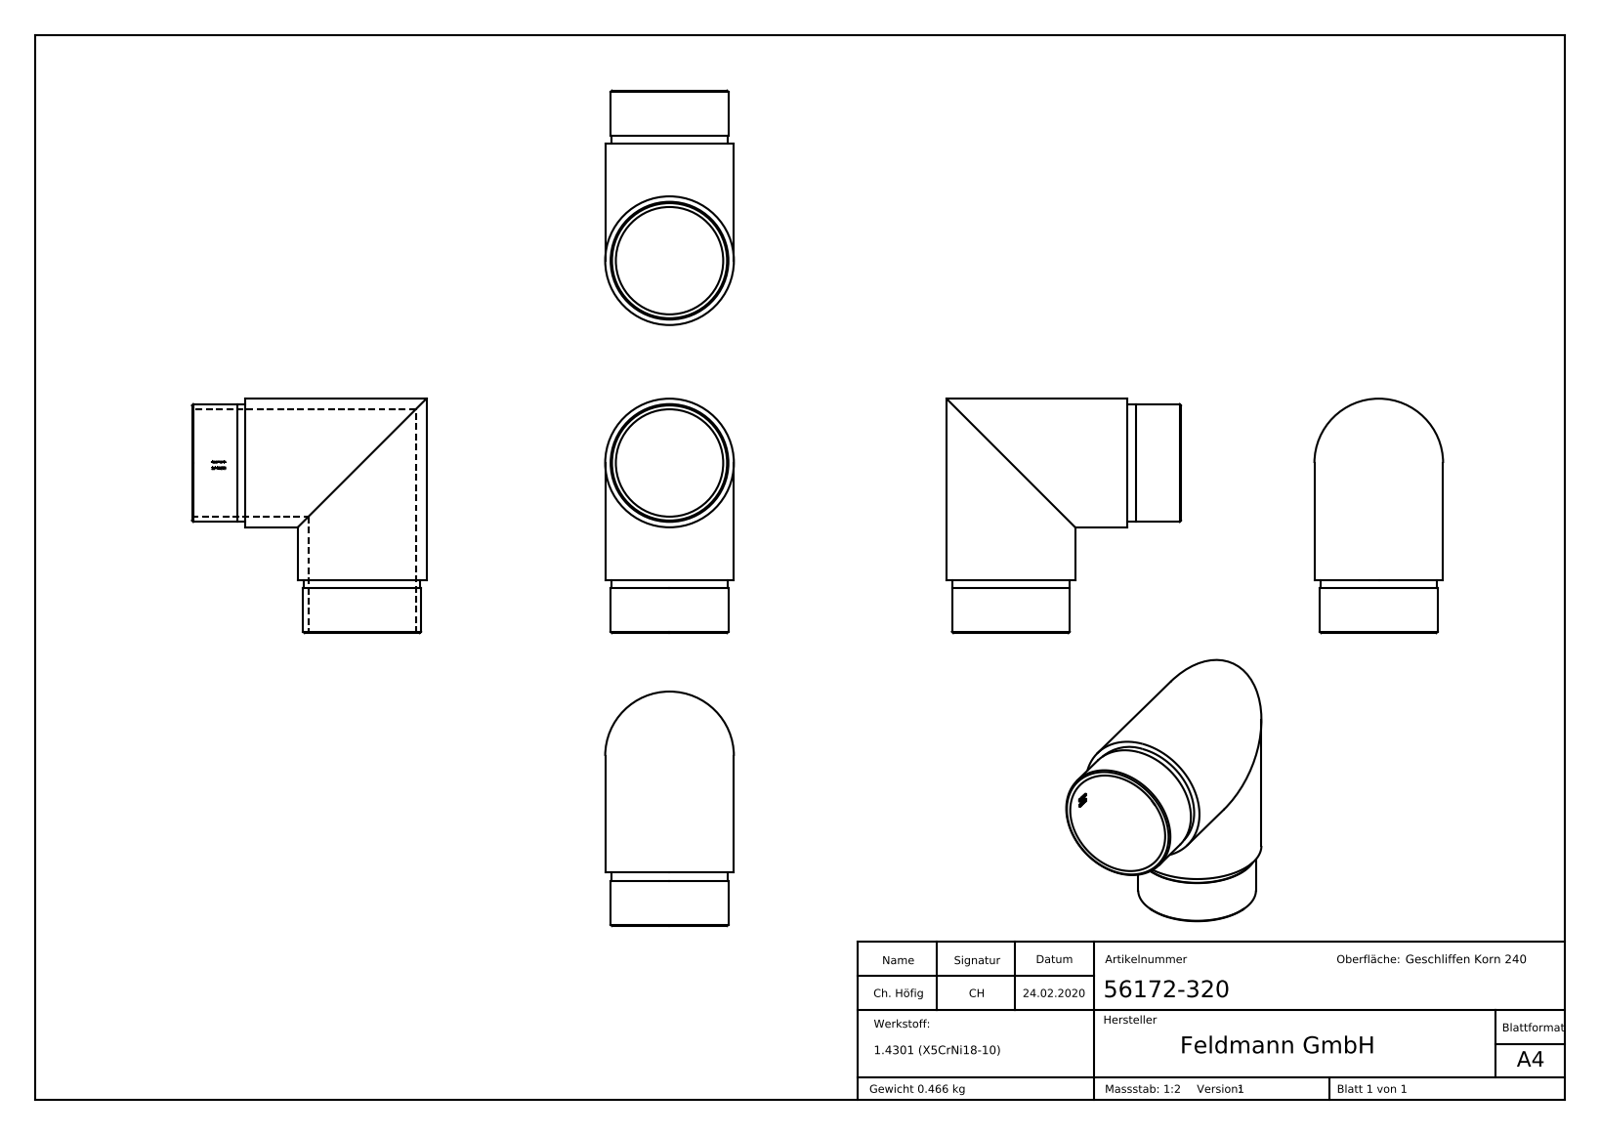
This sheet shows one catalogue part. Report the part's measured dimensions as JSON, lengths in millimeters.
{"part_name": "56172-320", "step_written_by": "SolidWorks 2015 (CONFIG_CONTROL_DESIGN)", "units": "millimeters", "bodies": {"solids": 1, "faces": 232, "planar": 100, "cylindrical": 30, "other": 102}, "overall_size": [88, 88, 48.3], "volume_mm3": 58974, "surface_area_mm2": 36169, "round_holes": [[40.3, 2]], "round_bosses_or_shafts": [[48.3, 2], [44.2, 2], [43.8, 2]], "partial_cylinders_radius": [[20.25, 1]], "face_to_face_distances": [20, 17, 3, 1.78, 0.83, 0.76, 0.79, 0.71, 0.99, 2.77]}
